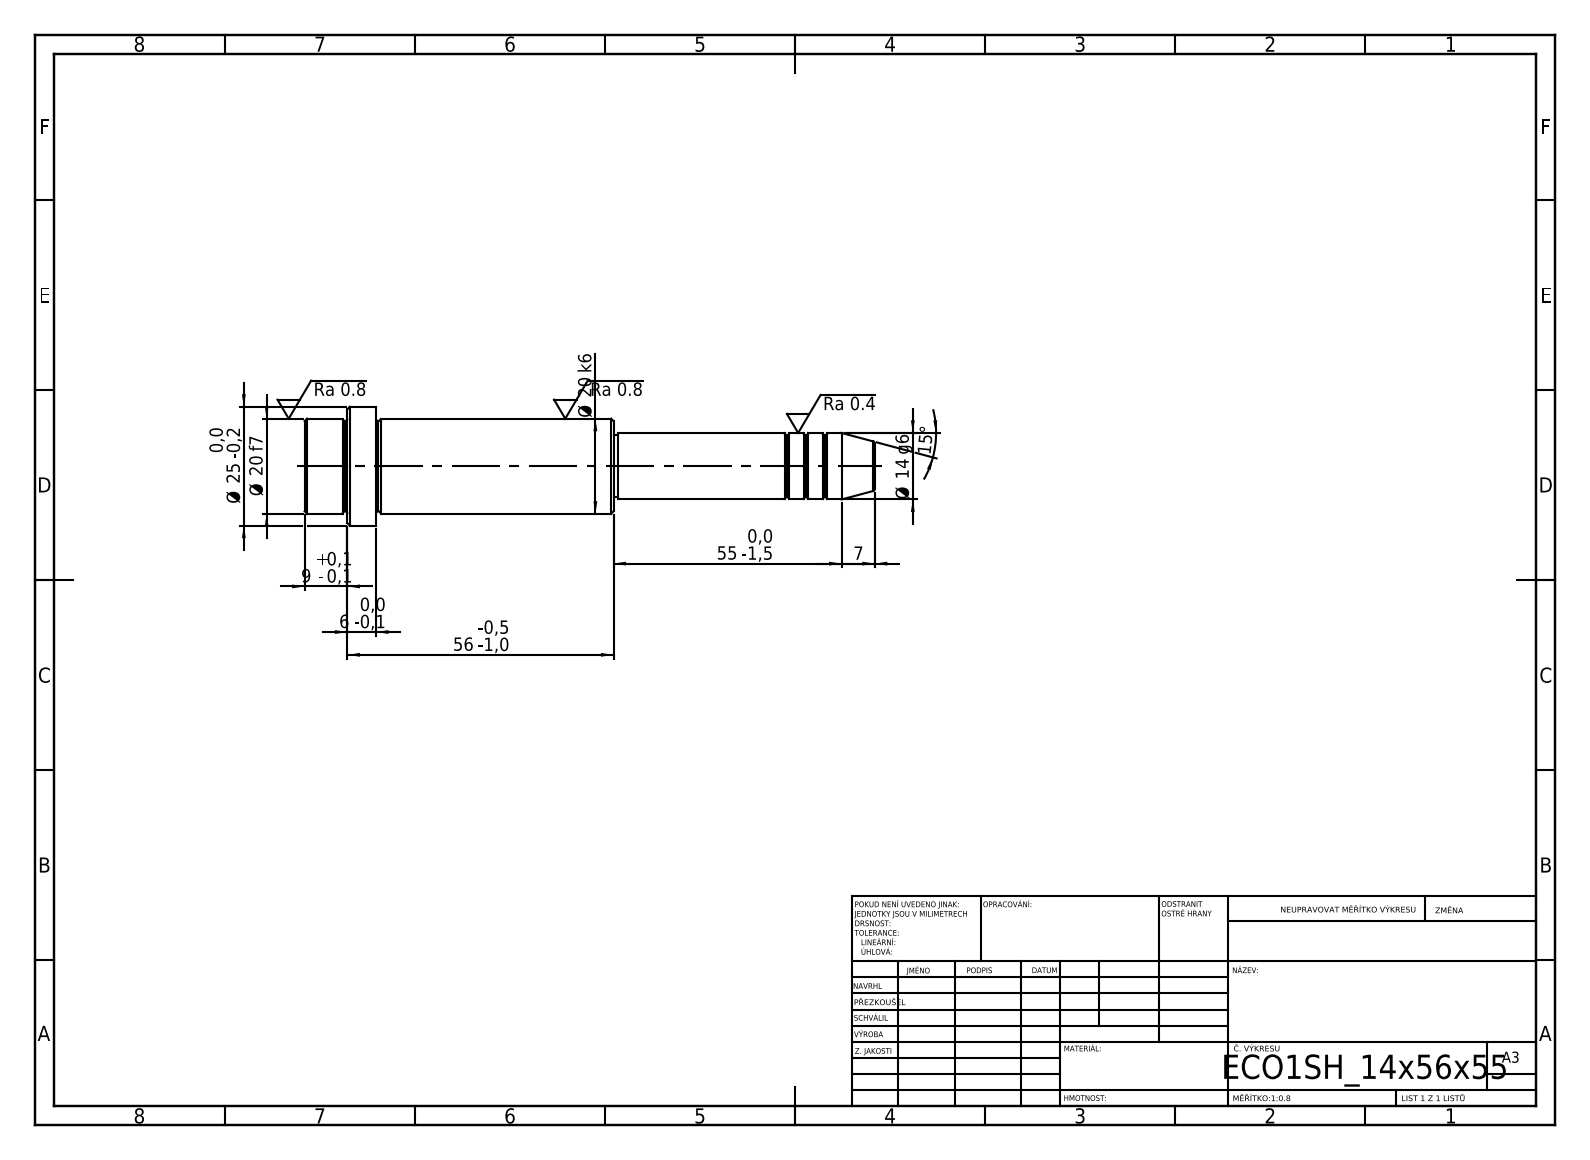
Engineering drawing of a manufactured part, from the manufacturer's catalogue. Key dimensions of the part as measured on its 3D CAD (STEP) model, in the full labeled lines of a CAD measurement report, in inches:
STEP written by: SolidWorks 2019 (CONFIG_CONTROL_DESIGN)
Units: inches
Bodies: 1 solid, 52 faces (6 planar, 16 cylindrical, 30 other)
Overall size (bounding box): 4.724 × 0.984 × 0.984
Volume: 1.803 in³ · Surface area: 11.75 in²
Round bosses / shafts (diameter × count): ⌀0.984 ×1, ⌀0.787 ×1, ⌀0.551 ×1, ⌀0.512 ×1
Main face-to-face distances: 0.591, 1.969, 2.559, 2.205, 0.236, 0.354, 2.165, 4.134, 4.37, 4.724
